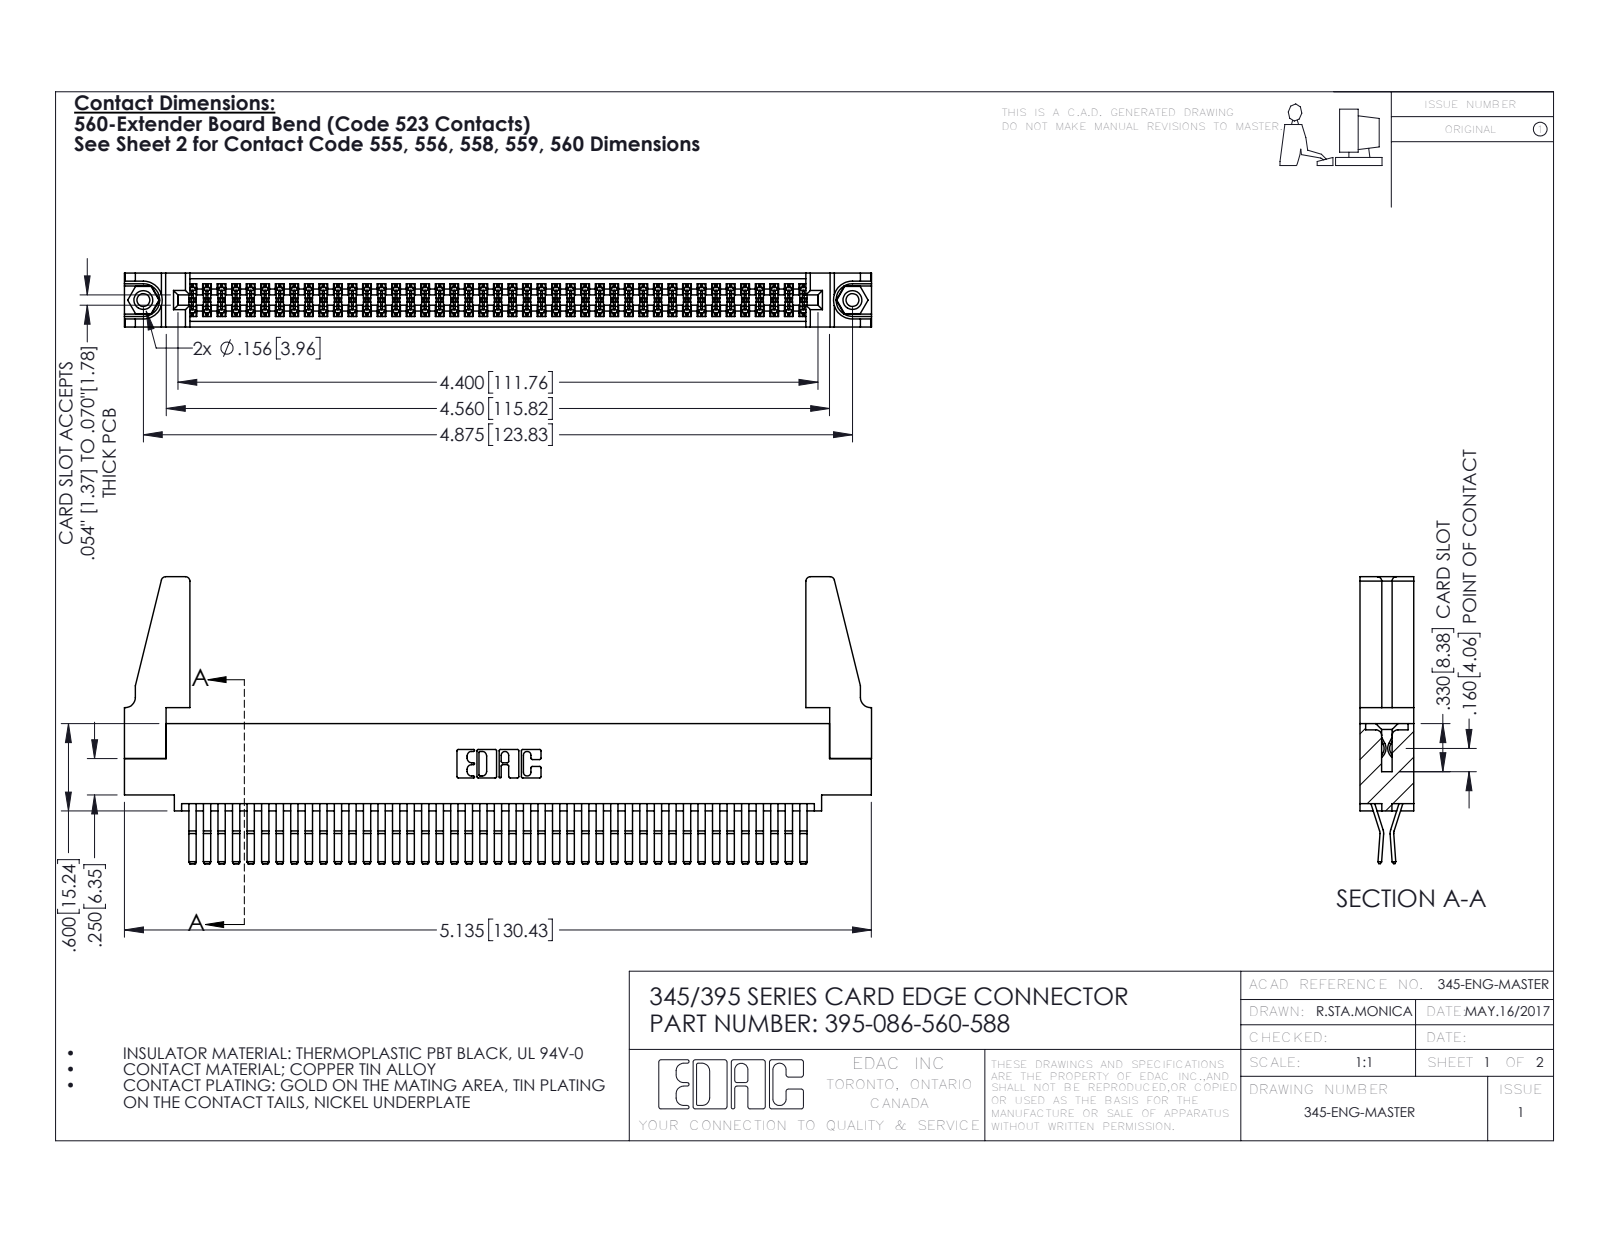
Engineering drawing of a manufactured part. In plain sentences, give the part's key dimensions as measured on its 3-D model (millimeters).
The part is named "395-086-560-588; 345-250-001_345-250-001-102; 345-292-001_560 Tail; 345-220-078_345-220-088 (+1 more)". Its 3-D file was written by "SolidWorks 2016 (CONFIG_CONTROL_DESIGN)". It is 91 solids with 4726 faces: 2994 planar, 1716 cylindrical and 16 other. Overall it measures 130.5 by 50.1 by 9.4 millimeters. Its volume is 16 420 cubic millimeters and its surface area 24 150 square millimeters. Round holes: 2 of diameter 2.3, 2 of diameter 3.2, 2 of diameter 4, 1 of diameter 1.6. Round bosses or shafts: 2 of diameter 3.9. Partial cylindrical surfaces (rounded edges, fillets, slot ends): 130 of radius 0.2, 22 of radius 0.3, 8 of radius 0.8, 6 of radius 0.2, 6 of radius 0.8, 3 of radius 0.7, 2 of radius 0.3, 2 of radius 0.4. The main face-to-face distances are 1.8, 7.6, 0.6, 9.4, 5.1, 2.5, 6.9, 5.7, 4.4, 3.8. The hole center spacings are 6.9, 117.8, 123.8.
